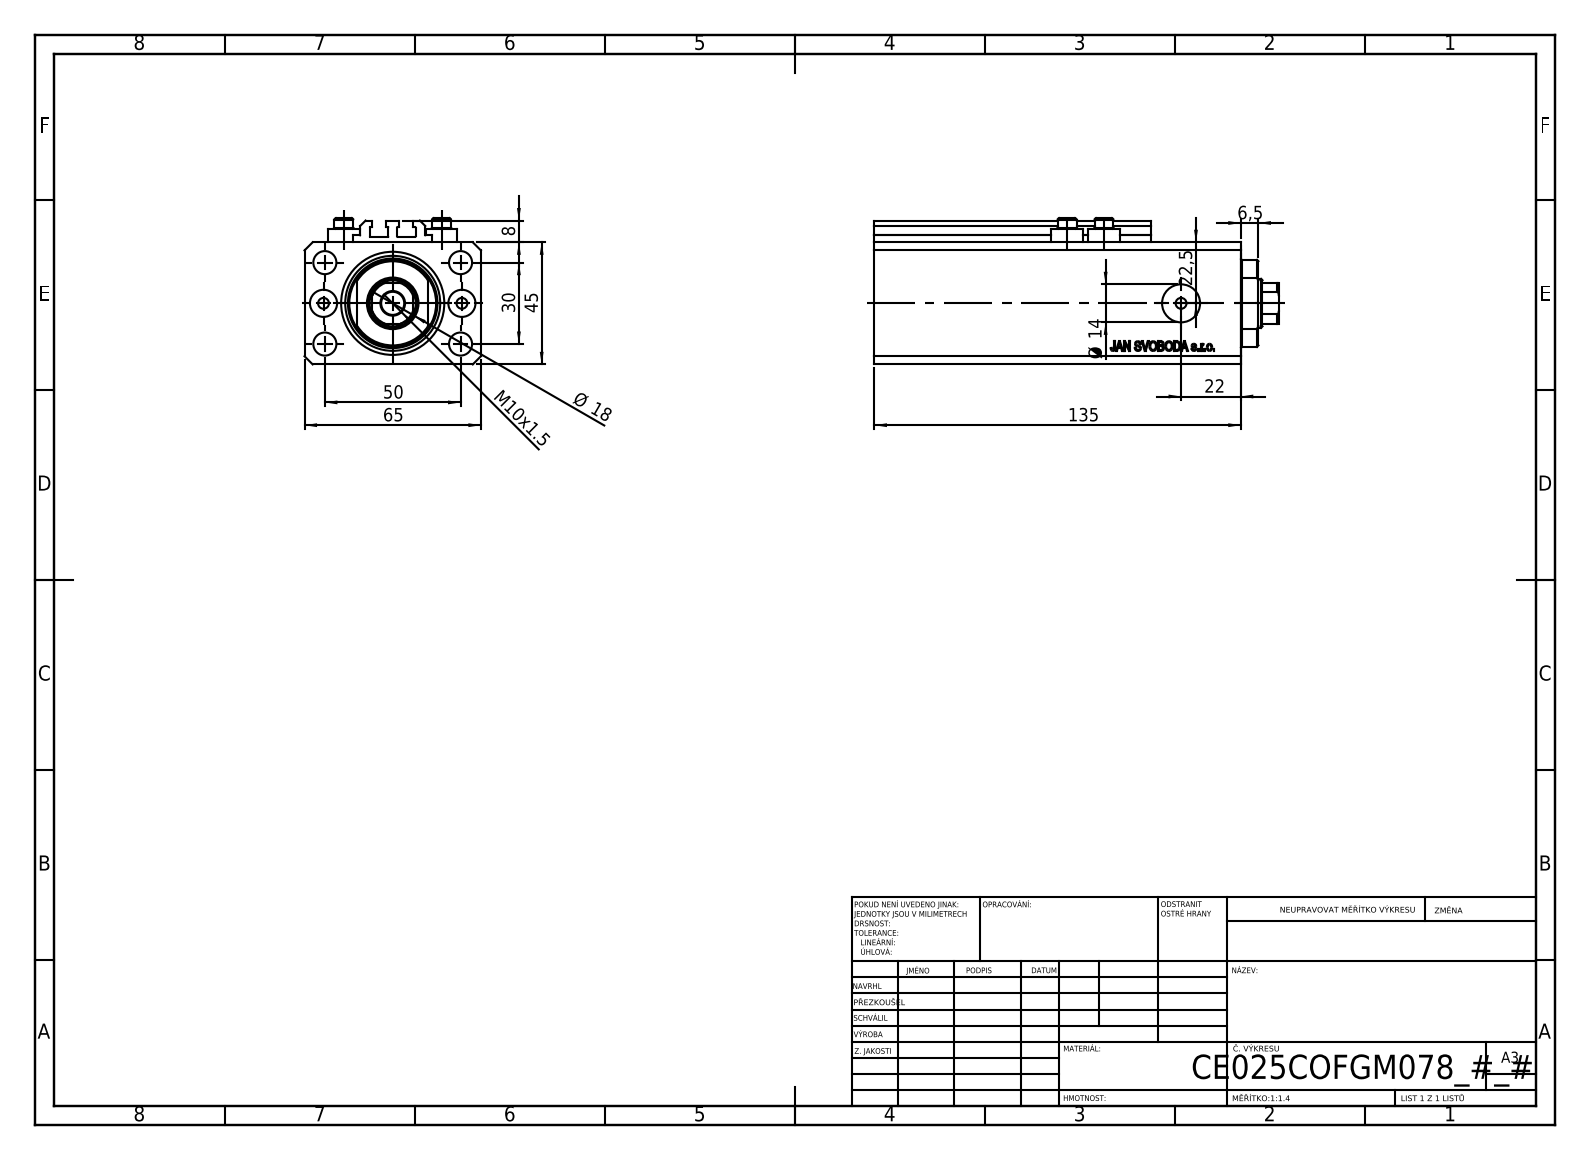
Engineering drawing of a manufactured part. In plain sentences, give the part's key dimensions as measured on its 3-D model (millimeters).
The part is named "V250CE_VC_C; V250CE_C_VCP; ALLEN BOLT V250CE; V250CE_C_Body". Its 3-D file was written by "SolidWorks 2019 (CONFIG_CONTROL_DESIGN)". It is 8 solids with 1034 faces: 504 planar, 86 cylindrical and 444 other. Overall it measures 149 by 65 by 54 millimeters. Its volume is 360 987 cubic millimeters and its surface area 89 495 square millimeters. Round holes: 8 of diameter 4, 5 of diameter 8.5, 2 of diameter 10, 2 of diameter 14, 1 of diameter 18, 1 of diameter 25, 1 of diameter 38. Round bosses or shafts: 4 of diameter 11.6, 4 of diameter 7. Partial cylindrical surfaces (rounded edges, fillets, slot ends): 10 of radius 0.2, 1 of radius 8.5, 1 of radius 16. The main face-to-face distances are 45, 65, 47, 14, 121, 135, 2.5, 2, 10, 20.5. The hole center spacings are 15.01, 29.15, 52.68, 13.6, 25.5, 30, 36, 38.48.
